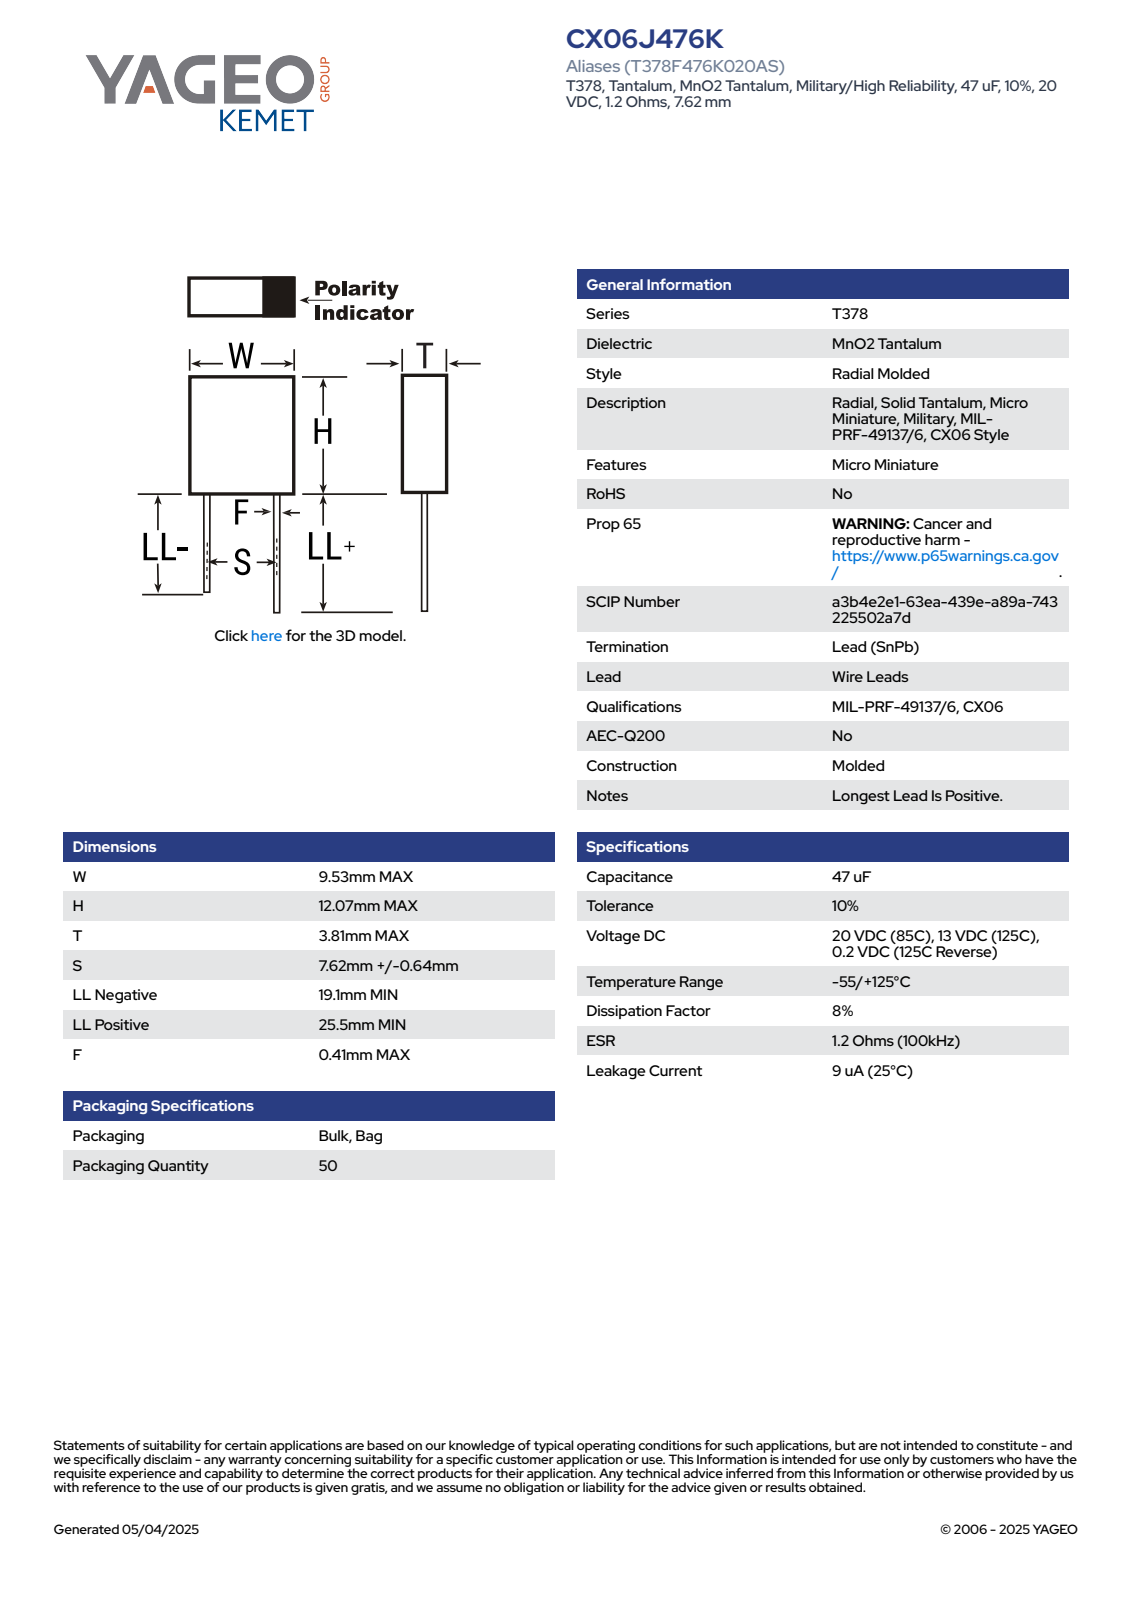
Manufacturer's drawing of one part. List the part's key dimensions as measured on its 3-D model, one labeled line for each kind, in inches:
Part name (STEP PRODUCT): CTRM_T378_W9.53H12.07T3.81S7.62LL44.46F0.44
STEP written by: SolidWorks 2014 (AUTOMOTIVE_DESIGN)
Units: inches
Bodies: 4 solids, 71 faces (67 planar, 4 cylindrical, 0 other)
Overall size (bounding box): 2.226 × 0.375 × 0.15
Volume: 0.028 in³ · Surface area: 0.812 in²
Round bosses / shafts (diameter × count): ⌀0.017 ×2
Main face-to-face distances: 0.15, 0.375, 0.475, 1.5, 1.976, 0.25, 1.75, 2.226, 0.206, 0.269
